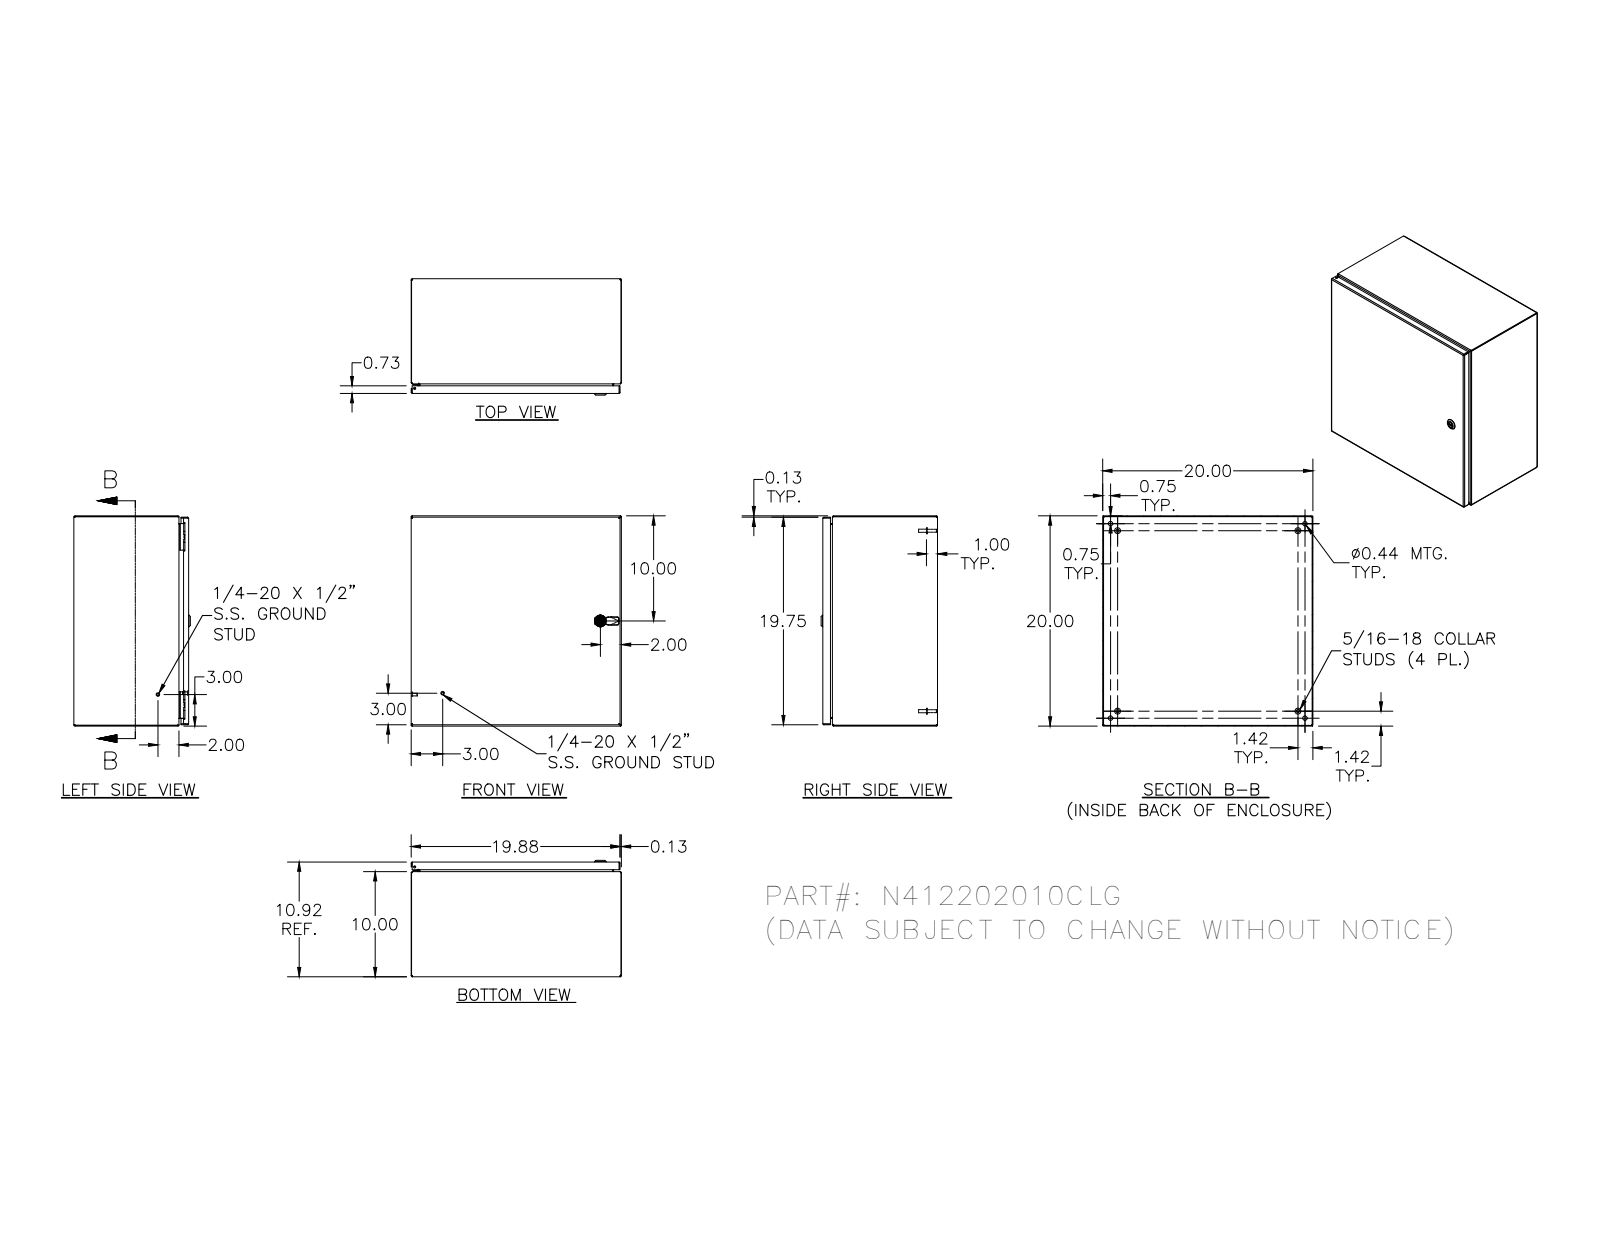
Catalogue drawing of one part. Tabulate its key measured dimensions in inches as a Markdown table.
| quantity | value |
| --- | --- |
| part name | N412202010CLG |
| STEP written by | SolidWorks 2018 (AUTOMOTIVE_DESIGN) |
| units | inches |
| bodies | 33 solids, 1449 faces (530 planar, 547 cylindrical, 372 other) |
| overall size | 20 × 20 × 11.075 |
| volume | 130.4 in³ |
| surface area | 3 544 in² |
| round holes (diameter × count) | 0.188 × 5, 0.093 × 4, 0.152 × 4, 0.167 × 4, 0.172 × 4, 0.437 × 4, 0.156 × 2, 0.187 × 1, 0.197 × 1, 0.315 × 1, 0.394 × 1, 0.402 × 1 |
| round bosses / shafts (diameter × count) | 0.25 × 10, 0.131 × 5, 0.563 × 4, 0.36 × 4, 0.32 × 4, 0.3 × 4, 0.275 × 4, 0.256 × 4 |
| partial cylindrical surfaces (radius × count) | 0.012 × 30, 0.031 × 30, 0.05 × 26, 0.105 × 20, 0.016 × 18, 0.125 × 16, 0.02 × 13, 0.032 × 8 |
| main face-to-face distances | 0.074, 10.843, 19.926, 19.852, 19.926, 20, 0.074, 10.769, 10.917, 0.917 |
| hole center spacings | 16, 0.66, 0.656, 1.307, 1.965, 15.34, 16.66, 18.5 |
